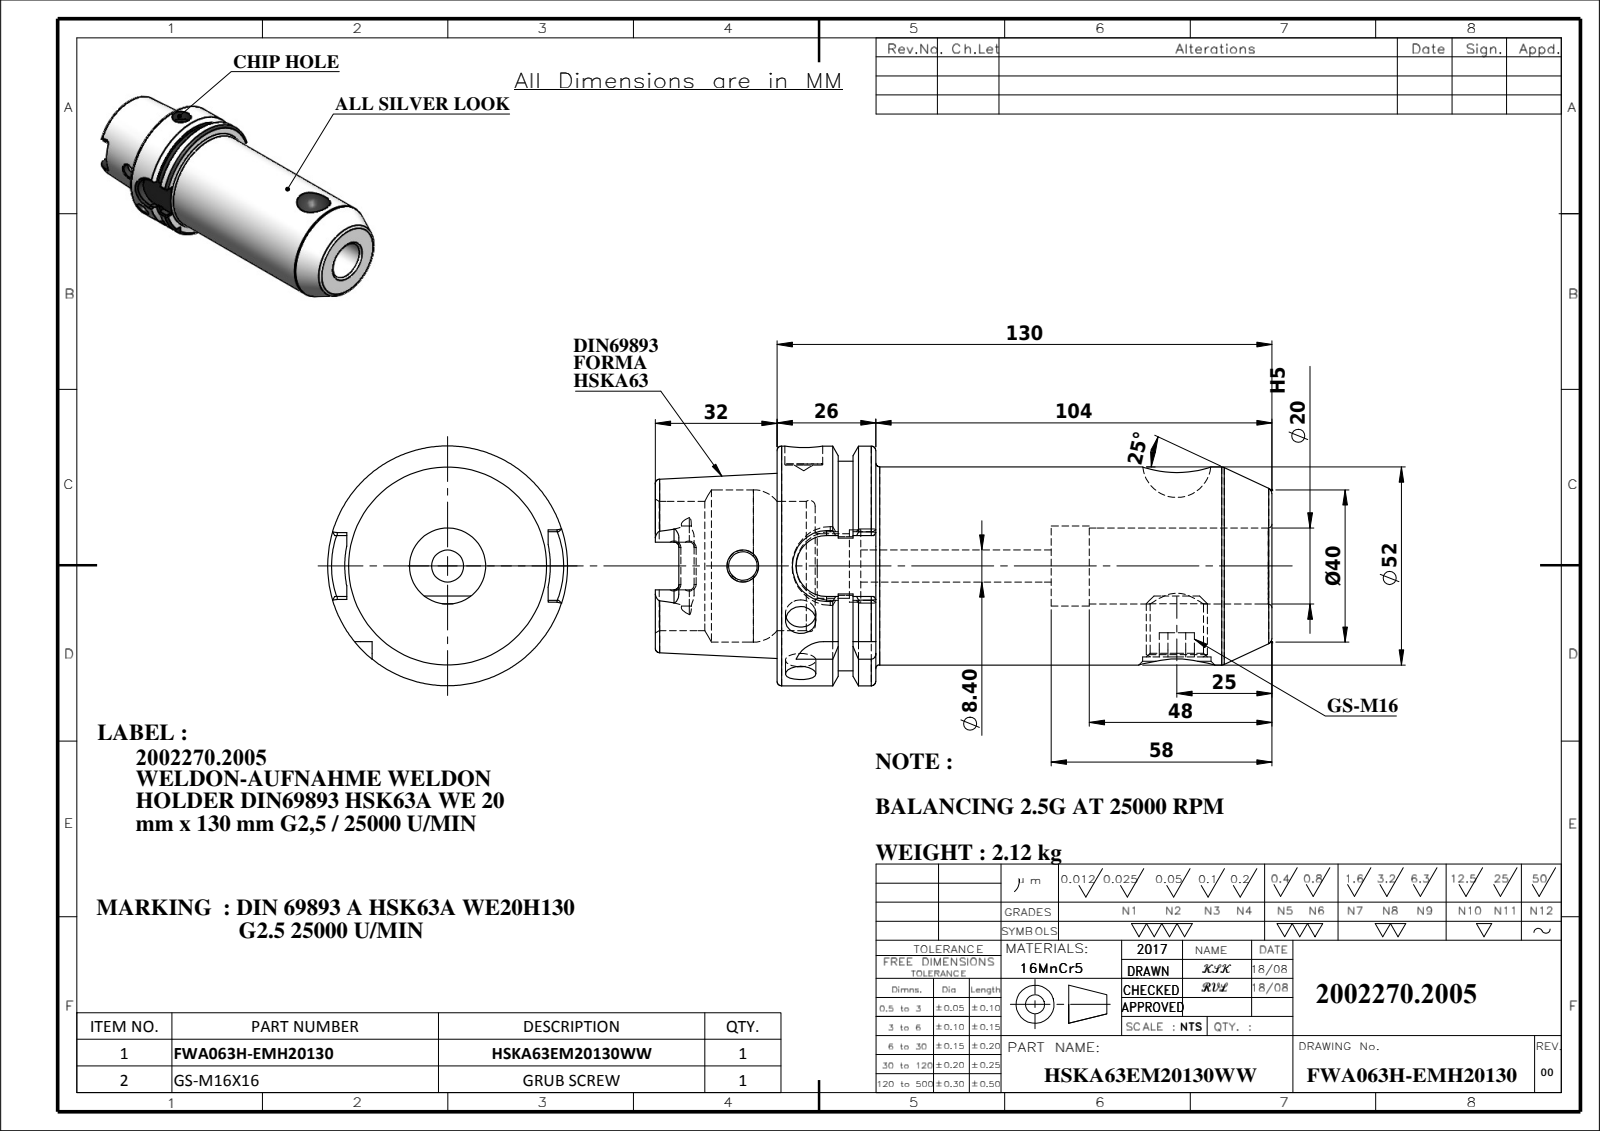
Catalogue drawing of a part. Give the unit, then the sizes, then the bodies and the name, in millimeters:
Units: millimetres
Overall size (bounding box): 162 × 63 × 63
Round holes (diameter × count): ⌀8 ×2, ⌀7.5 ×1, ⌀8.4 ×1, ⌀10 ×1, ⌀14 ×1, ⌀17 ×1, ⌀18 ×1, ⌀19 ×1, ⌀20 ×1, ⌀21 ×1, ⌀34 ×1, ⌀40 ×1
Round bosses / shafts (diameter × count): ⌀63 ×1, ⌀55 ×1, ⌀52 ×1, ⌀16 ×1
Partial cylindrical surfaces — rounded edges, fillets, slot ends (radius × count): R1.3 ×6, R2.88 ×4, R8 ×2, R9 ×1
Main face-to-face distances: 130, 10, 120, 25.95, 15.95, 104.05, 32, 42, 57.95, 162
Hole centre spacings: 98
Volume: 273 736 mm³ · Surface area: 45 108 mm²
Bodies: 2 solids, 197 faces (64 planar, 57 cylindrical, 76 other)
Part name (STEP PRODUCT): GS-M16X16-DIN1835-B_ISO 4026 - M16 x 10-N; 9163A-WE820130; HSKA63EM20130WW
STEP written by: SolidWorks 2018 (CONFIG_CONTROL_DESIGN)
